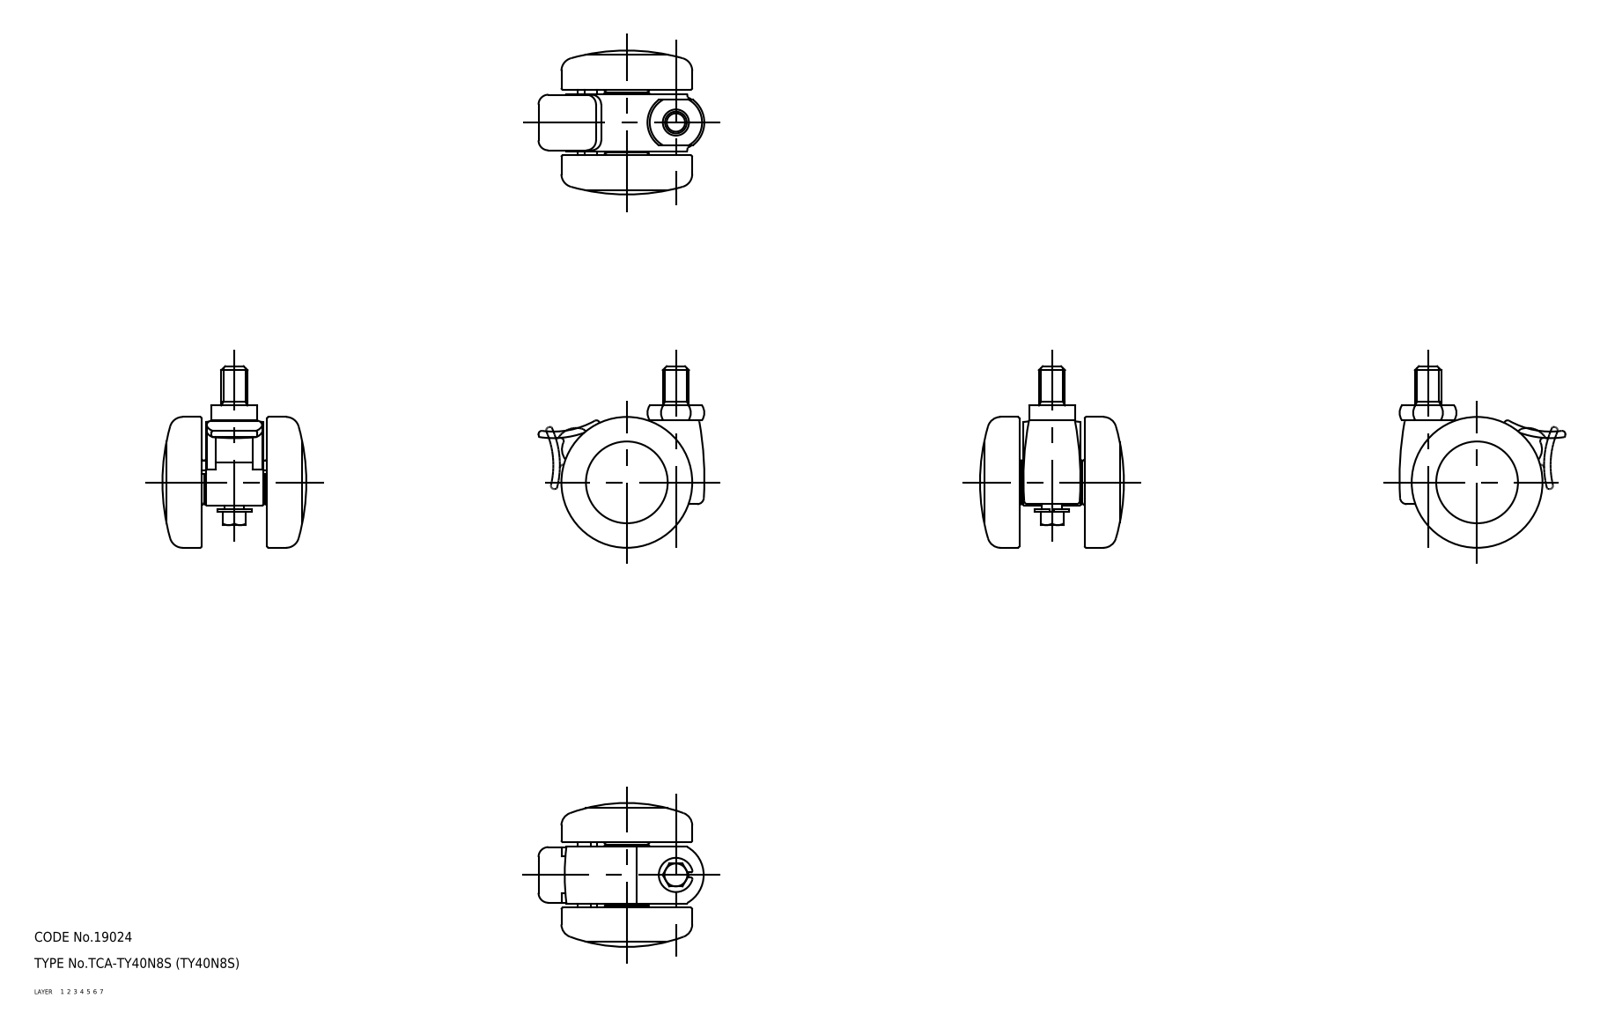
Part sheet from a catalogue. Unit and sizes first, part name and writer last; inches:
Units: inches
Overall size (bounding box): 2.185 × 1.997 × 1.732
Volume: 2.41 in³ · Surface area: 29.51 in²
Bodies: 5 solids, 193 faces (0 planar, 0 cylindrical, 193 other)
Part name (STEP PRODUCT): wheel; main shaft; lever; TY40N8S_10613_36
STEP written by: CADfix (AUTOMOTIVE_DESIGN)
